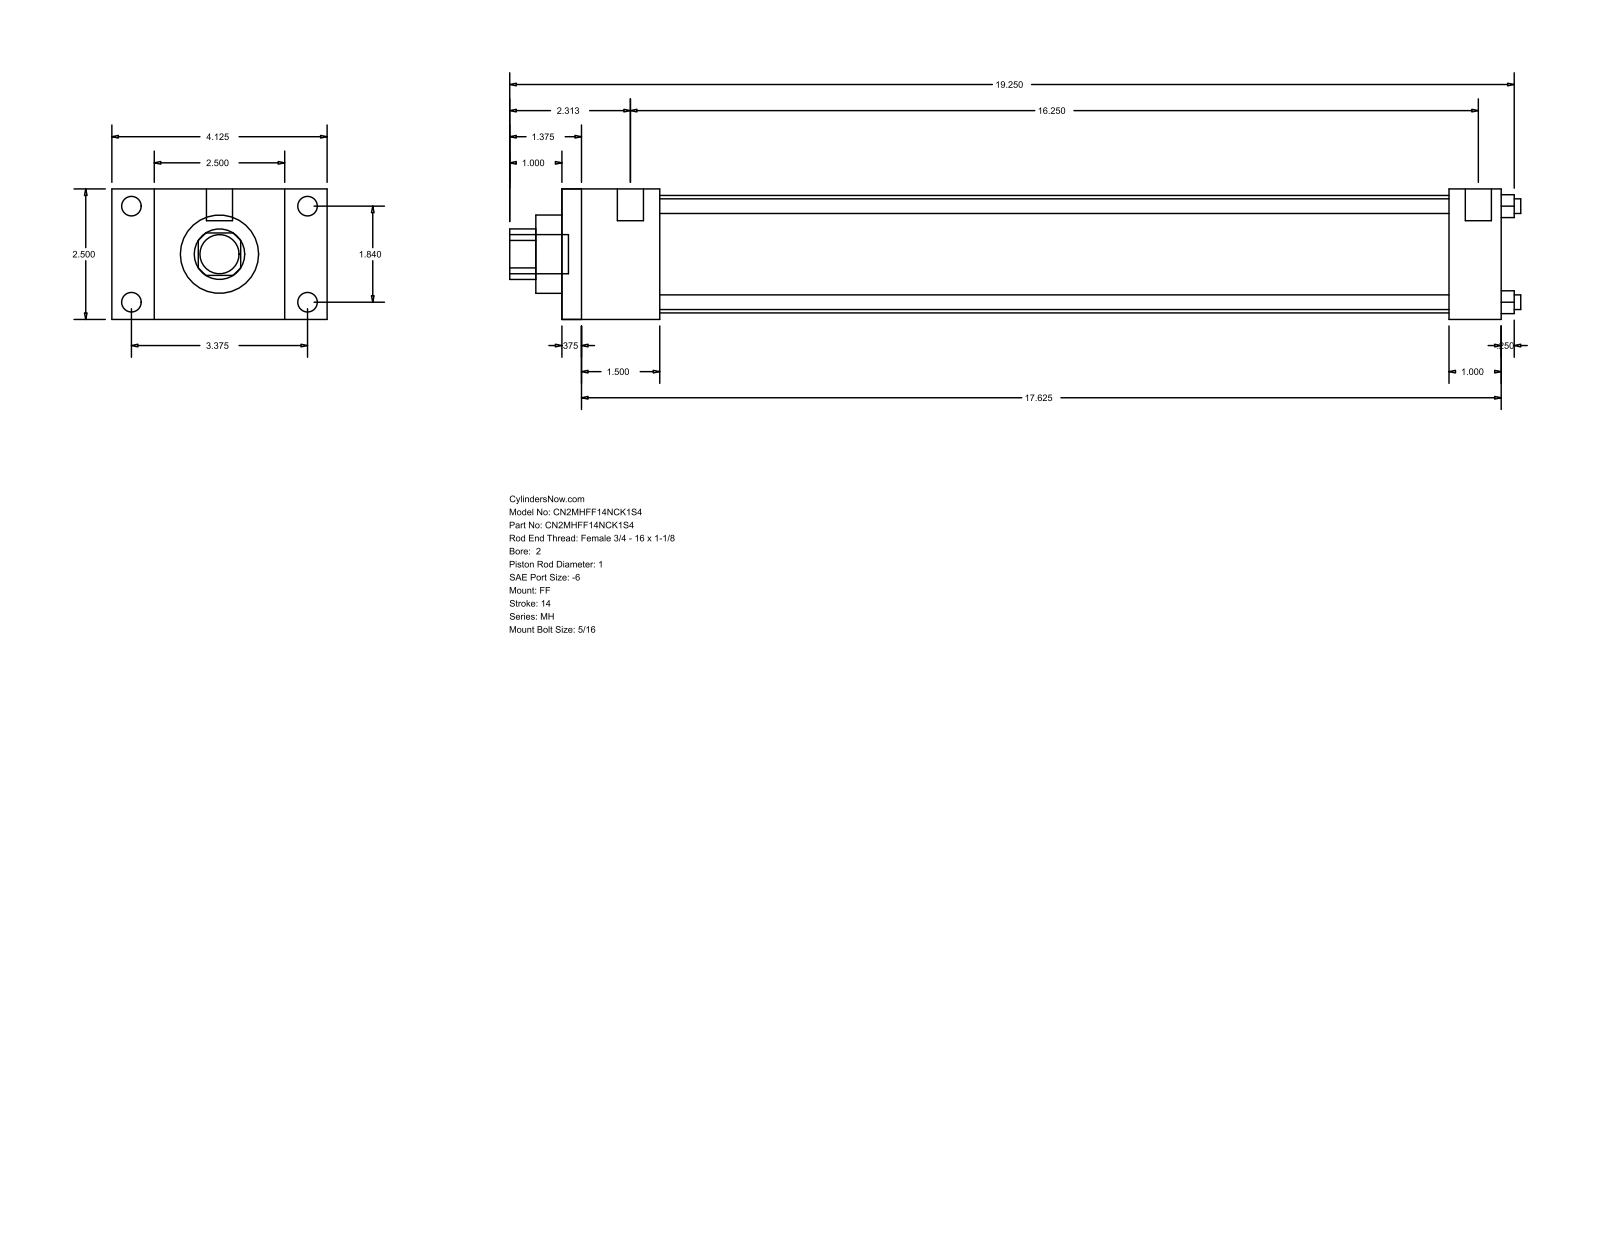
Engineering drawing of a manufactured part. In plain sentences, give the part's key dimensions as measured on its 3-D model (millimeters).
The part is named "MH_FF__0200_1". Its 3-D file was written by "GSSL Pune (CONFIG_CONTROL_DESIGN)". It is 0 solids with 92 faces: 64 planar, 28 cylindrical and 0 other. Overall it measures 492.12 by 104.78 by 63.5 millimeters. Round holes: 4 of diameter 7.14, 1 of diameter 25.4, 1 of diameter 38.1, 1 of diameter 57.15. Round bosses or shafts: 4 of diameter 9.53, 4 of diameter 5.56, 2 of diameter 12.7, 1 of diameter 19.05. Partial cylindrical surfaces (rounded edges, fillets, slot ends): 1 of radius 12.29. The main face-to-face distances are 63.5, 457.2, 9.52, 447.68, 20.64, 25.4, 47.63, 431.8, 38.11, 422.28. The hole center spacings are 33.05, 46.74, 66.1.
